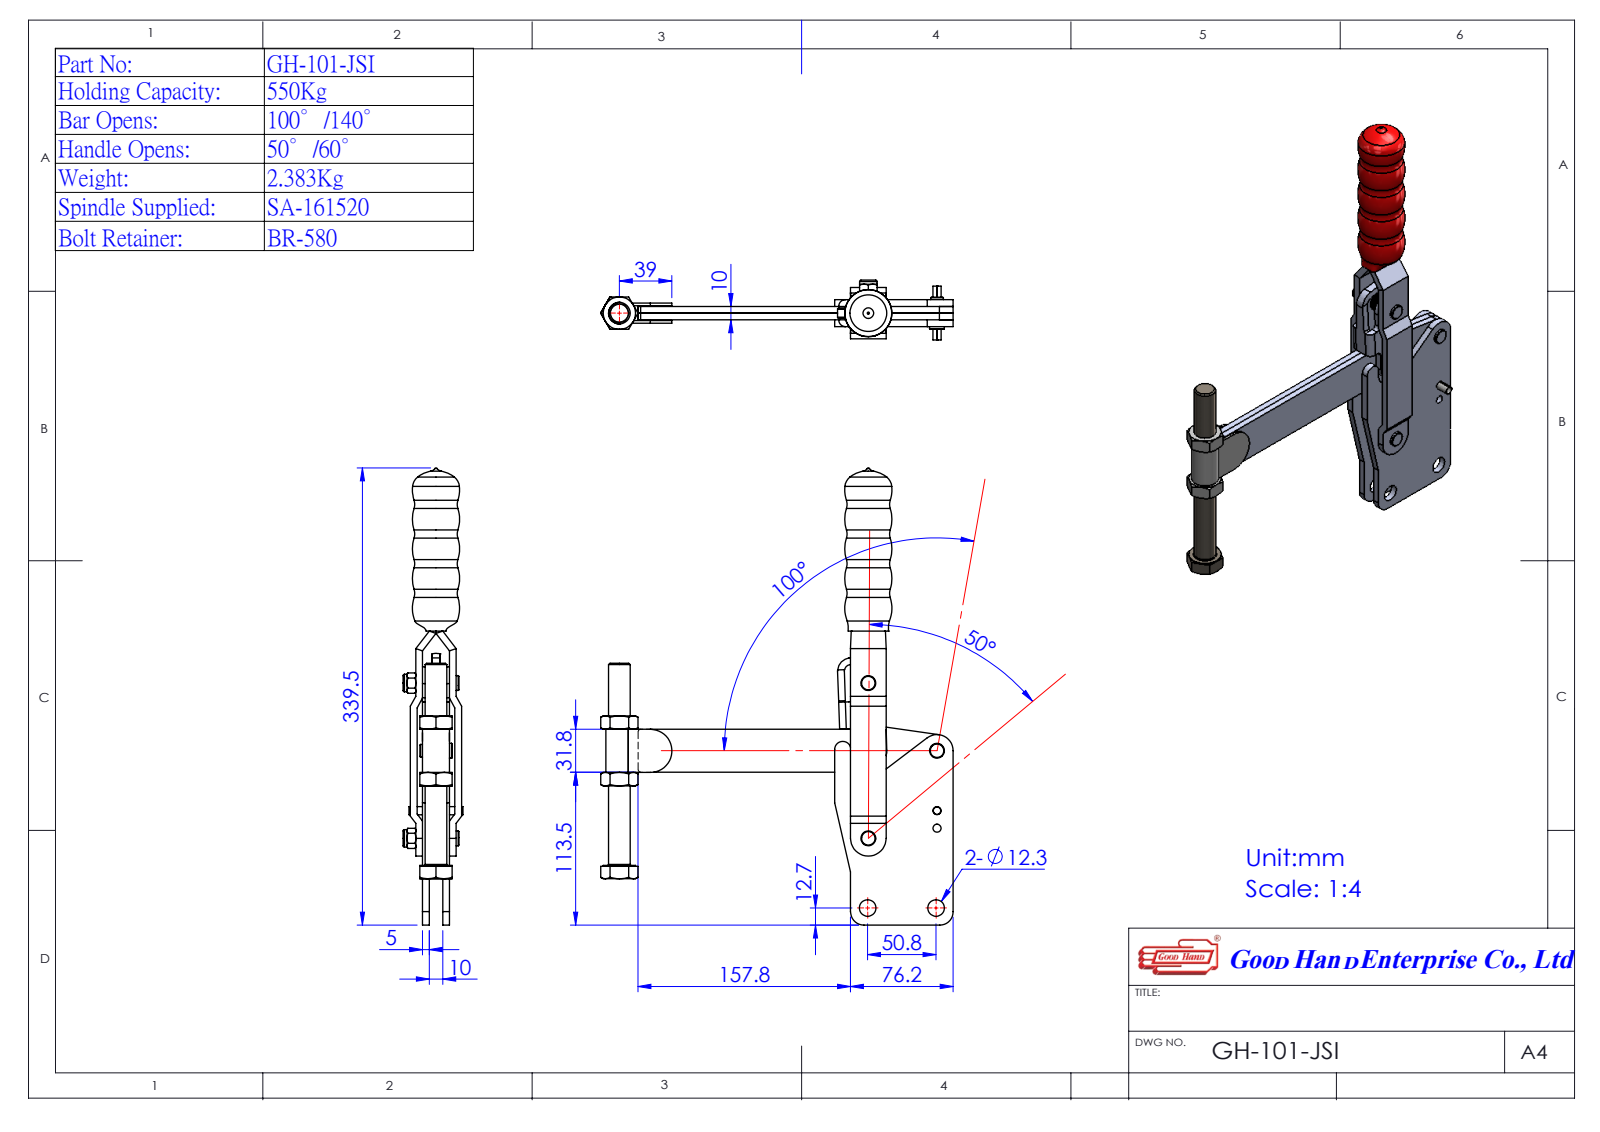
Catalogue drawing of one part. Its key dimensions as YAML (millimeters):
part_name: "Group1^GH-101-JSB(簡化)-1; Group6^GH-101-JSB(簡化)-1; Group4^GH-101-JSB(簡化)-1; GH-101-JSB(簡化)-1 (+2 more)"
step_written_by: "SolidWorks 2016 (AUTOMOTIVE_DESIGN)"
units: millimeters
bodies: {solids: 4, faces: 331, planar: 138, cylindrical: 113, other: 80}
overall_size: [339.2, 277.52, 40]
volume: 245424
surface_area: 129204
round_holes:
  - {diameter: 6, count: 5}
  - {diameter: 12.3, count: 2}
  - {diameter: 5.5, count: 1}
round_bosses_or_shafts:
  - {diameter: 11, count: 4}
  - {diameter: 8, count: 2}
  - {diameter: 7.94, count: 2}
  - {diameter: 24, count: 1}
  - {diameter: 16, count: 1}
  - {diameter: 6, count: 1}
partial_cylinders:
  - {radius: 1, count: 4}
  - {radius: 12, count: 3}
  - {radius: 2, count: 2}
  - {radius: 3, count: 2}
  - {radius: 5, count: 2}
  - {radius: 10, count: 2}
  - {radius: 11, count: 2}
  - {radius: 6, count: 1}
face_to_face_distances: [5, 15, 10, 20, 24, 9, 4, 29, 14, 33]
hole_center_spacings: [13, 44.48, 49.25, 50.23, 50.8, 51.55, 51.7, 54.97]
